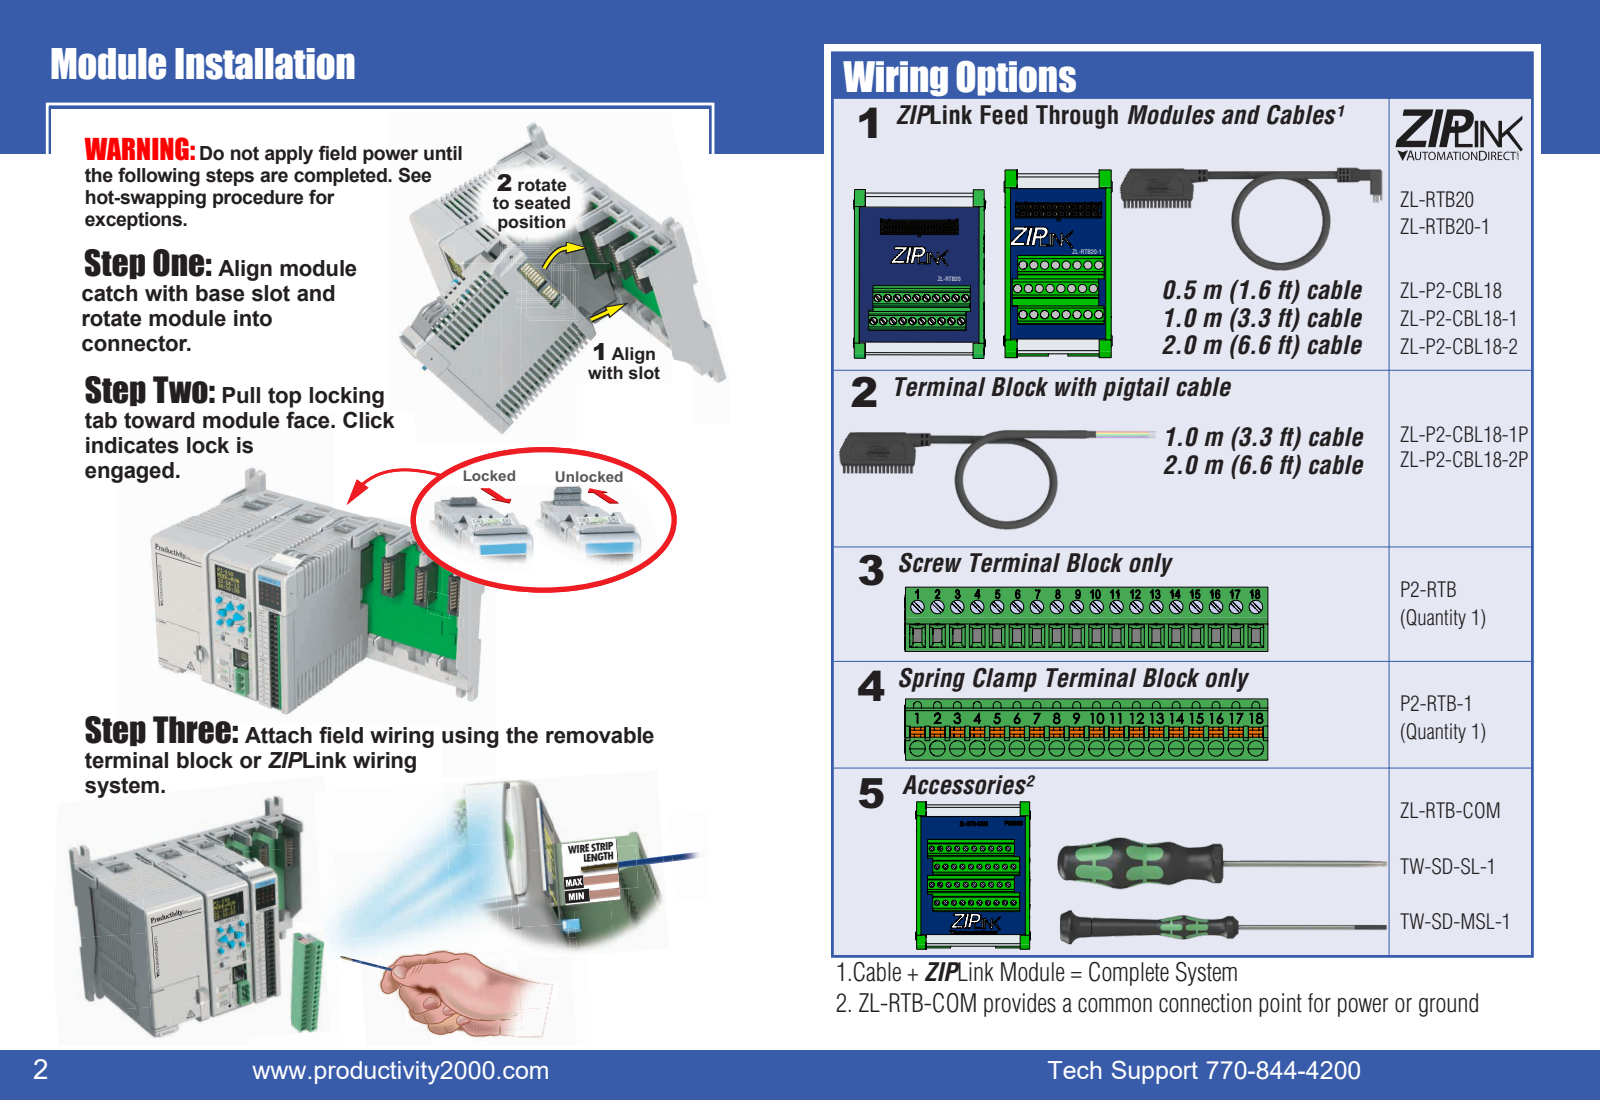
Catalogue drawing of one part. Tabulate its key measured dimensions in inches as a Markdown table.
| quantity | value |
| --- | --- |
| part name | P2-16TD-TTL |
| STEP written by | SolidWorks 2021 (AUTOMOTIVE_DESIGN) |
| units | inches |
| bodies | 7 solids, 4274 faces (2390 planar, 884 cylindrical, 1000 other) |
| overall size | 4.116 × 4.004 × 0.93 |
| volume | 13.12 in³ |
| surface area | 64.89 in² |
| round holes (diameter × count) | 0.016 × 16, 0.063 × 13, 0.049 × 3, 0.016 × 2, 0.059 × 1, 0.079 × 1, 0.083 × 1, 0.098 × 1 |
| partial cylindrical surfaces (radius × count) | 0.02 × 323, 0.008 × 76, 0.039 × 64, 0.059 × 22, 0.062 × 18, 0.063 × 13, 0.008 × 6, 0.079 × 6 |
| main face-to-face distances | 0.93, 0.063, 0.928, 0.927, 0.928, 0.867, 3.948, 0.025, 0.867, 3.946 |
| hole center spacings | 0.6, 0.15, 0.6, 0.75, 0.2, 0.4, 0.45, 0.3 |
